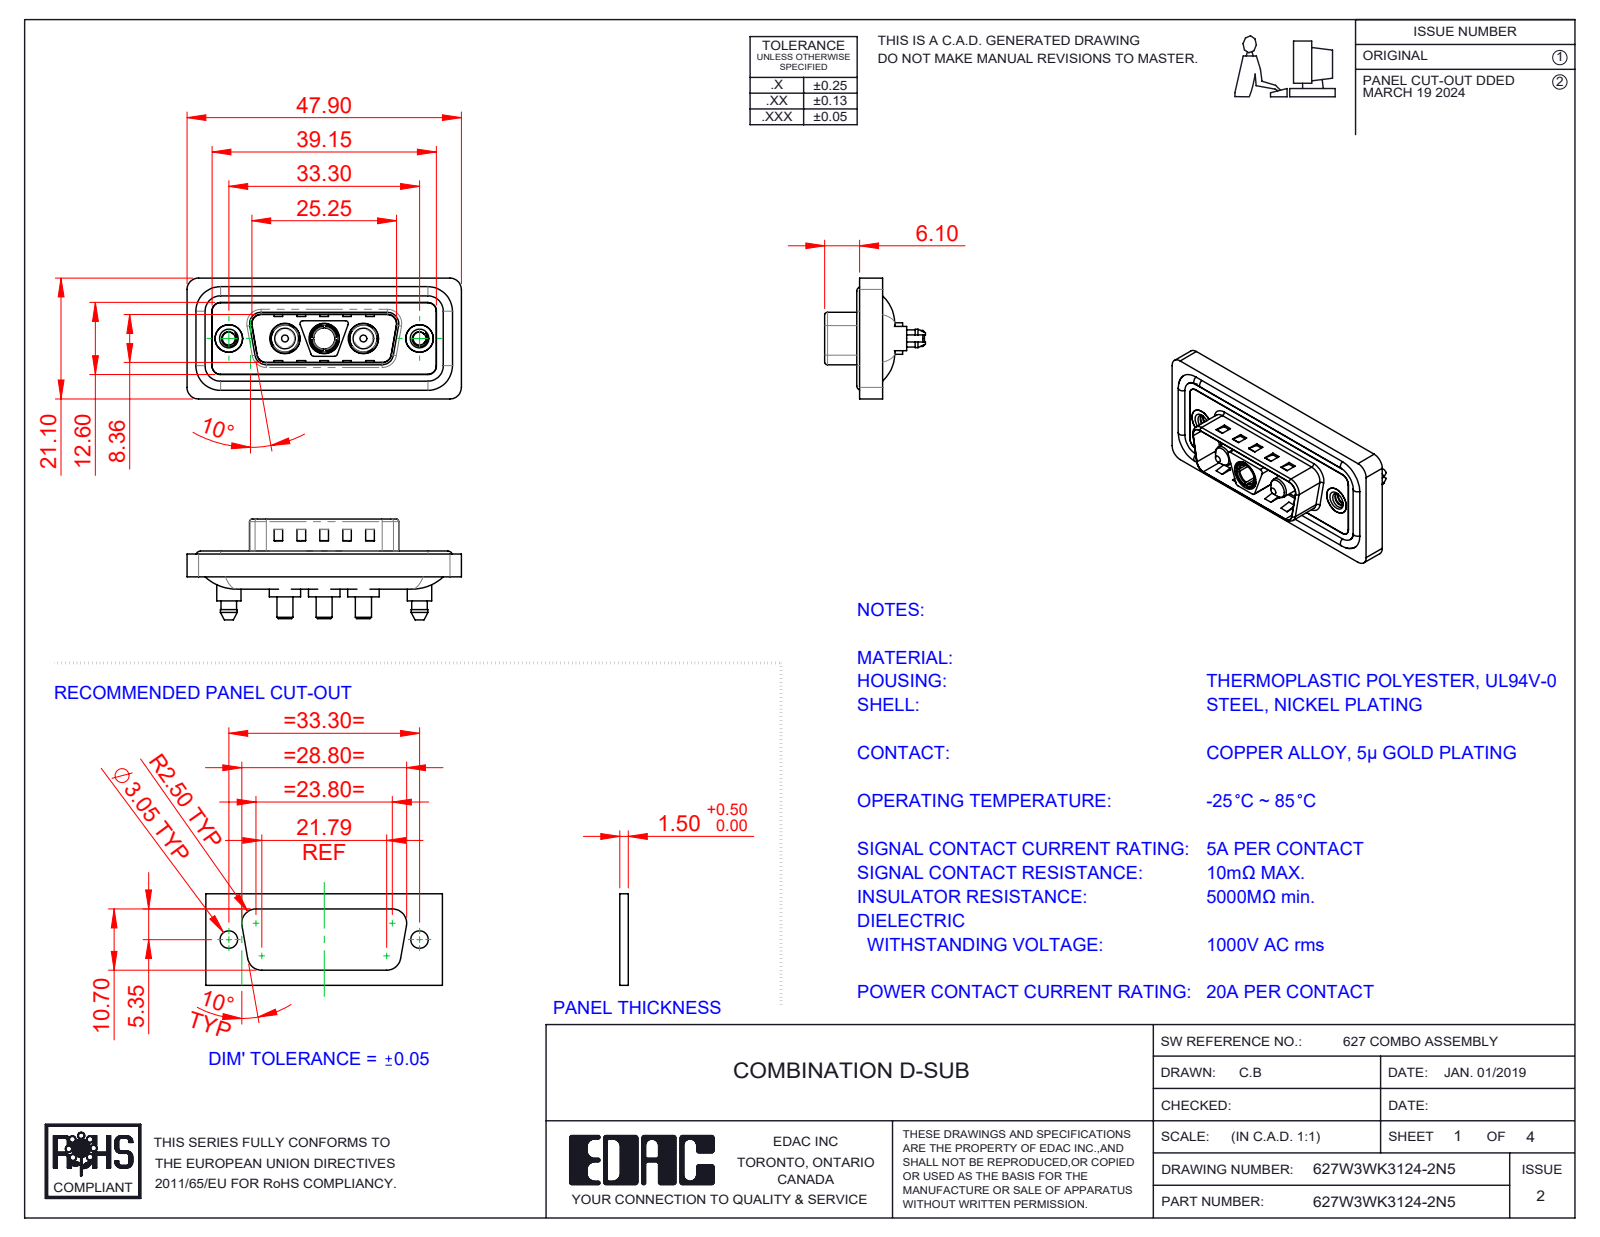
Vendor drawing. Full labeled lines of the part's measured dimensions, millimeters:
Part name (STEP PRODUCT): Power Socket_20A S; 627Combo Shell Front_15 Contacts; 627W3WK3124-2N5; 627Combo Shell Rear_15 Contacts (+4 more)
STEP written by: SolidWorks 2023 (CONFIG_CONTROL_DESIGN)
Units: millimetres
Bodies: 13 solids, 659 faces (247 planar, 282 cylindrical, 130 other)
Overall size (bounding box): 47.9 × 21.1 × 17.6
Volume: 5 822 mm³ · Surface area: 9 460 mm²
Round holes (diameter × count): ⌀4.85 ×3, ⌀5.3 ×3, ⌀2.26 ×2, ⌀4 ×2, ⌀4.8 ×2, ⌀5 ×2, ⌀3.7 ×1
Round bosses / shafts (diameter × count): ⌀1.6 ×4, ⌀5.5 ×3, ⌀5.2 ×3, ⌀4.75 ×3, ⌀3.75 ×3, ⌀2.8 ×3, ⌀5.4 ×2, ⌀4.9 ×2
Partial cylindrical surfaces — rounded edges, fillets, slot ends (radius × count): R1.5 ×28, R2 ×20, R0.5 ×12, R1.6 ×10, R0.25 ×4, R0.6 ×4, R0.65 ×4, R0.9 ×4
Main face-to-face distances: 0.4, 1.1, 1.5, 0.5, 1.6, 3.1, 2.9, 4, 0.7, 0.82
Hole centre spacings: 6.85, 9.8, 16.65, 23.5, 13.7, 33.3
